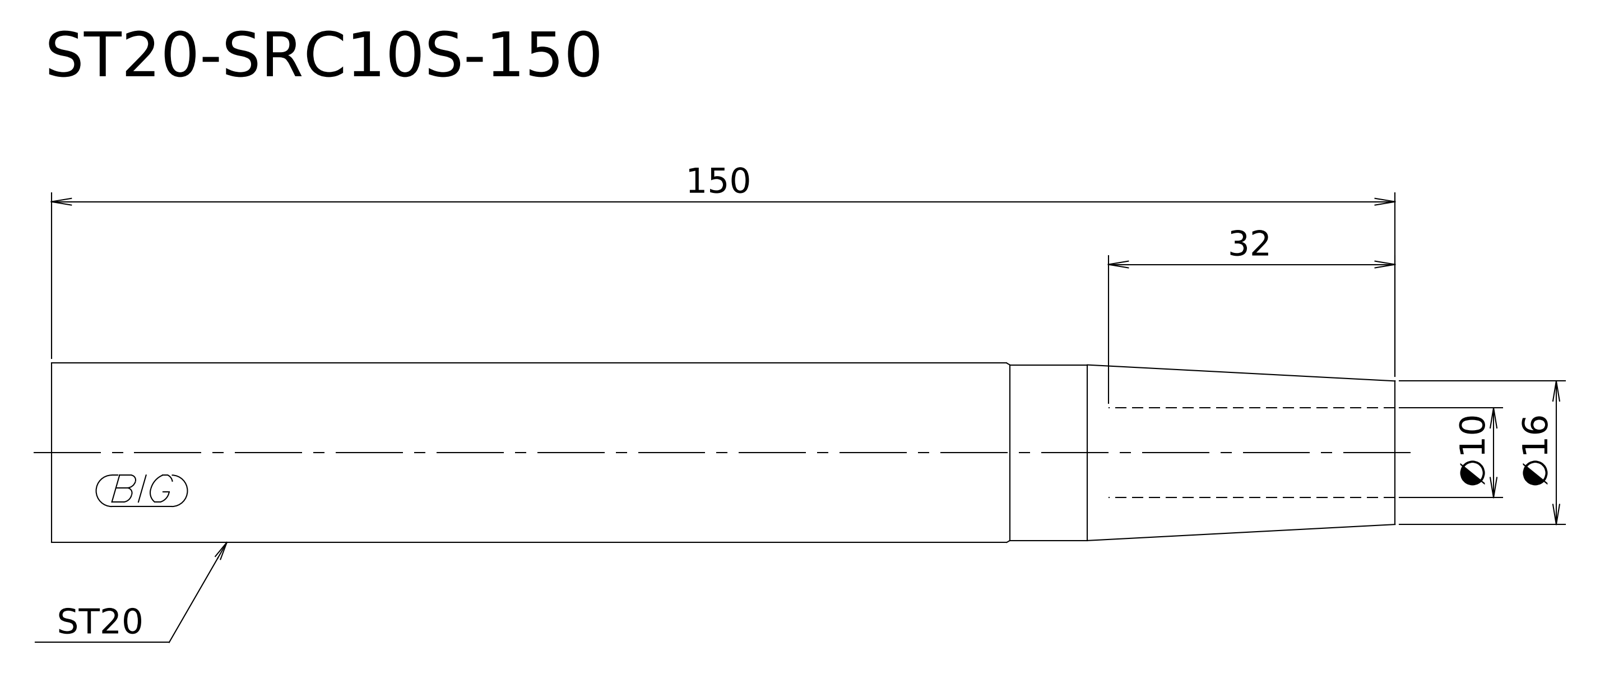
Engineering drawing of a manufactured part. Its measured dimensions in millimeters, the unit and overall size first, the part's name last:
Units: millimetres
Overall size (bounding box): 150 × 20 × 20
Round bosses / shafts (diameter × count): ⌀20 ×1, ⌀19.6 ×1
Main face-to-face distances: 150
Volume: 44 800 mm³ · Surface area: 9 697 mm²
Bodies: 1 solid, 6 faces (2 planar, 2 cylindrical, 2 other)
STEP written by: Kubotek KeyCreator V8.5.1 (14335) (CONFIG_CONTROL_DESIGN)
